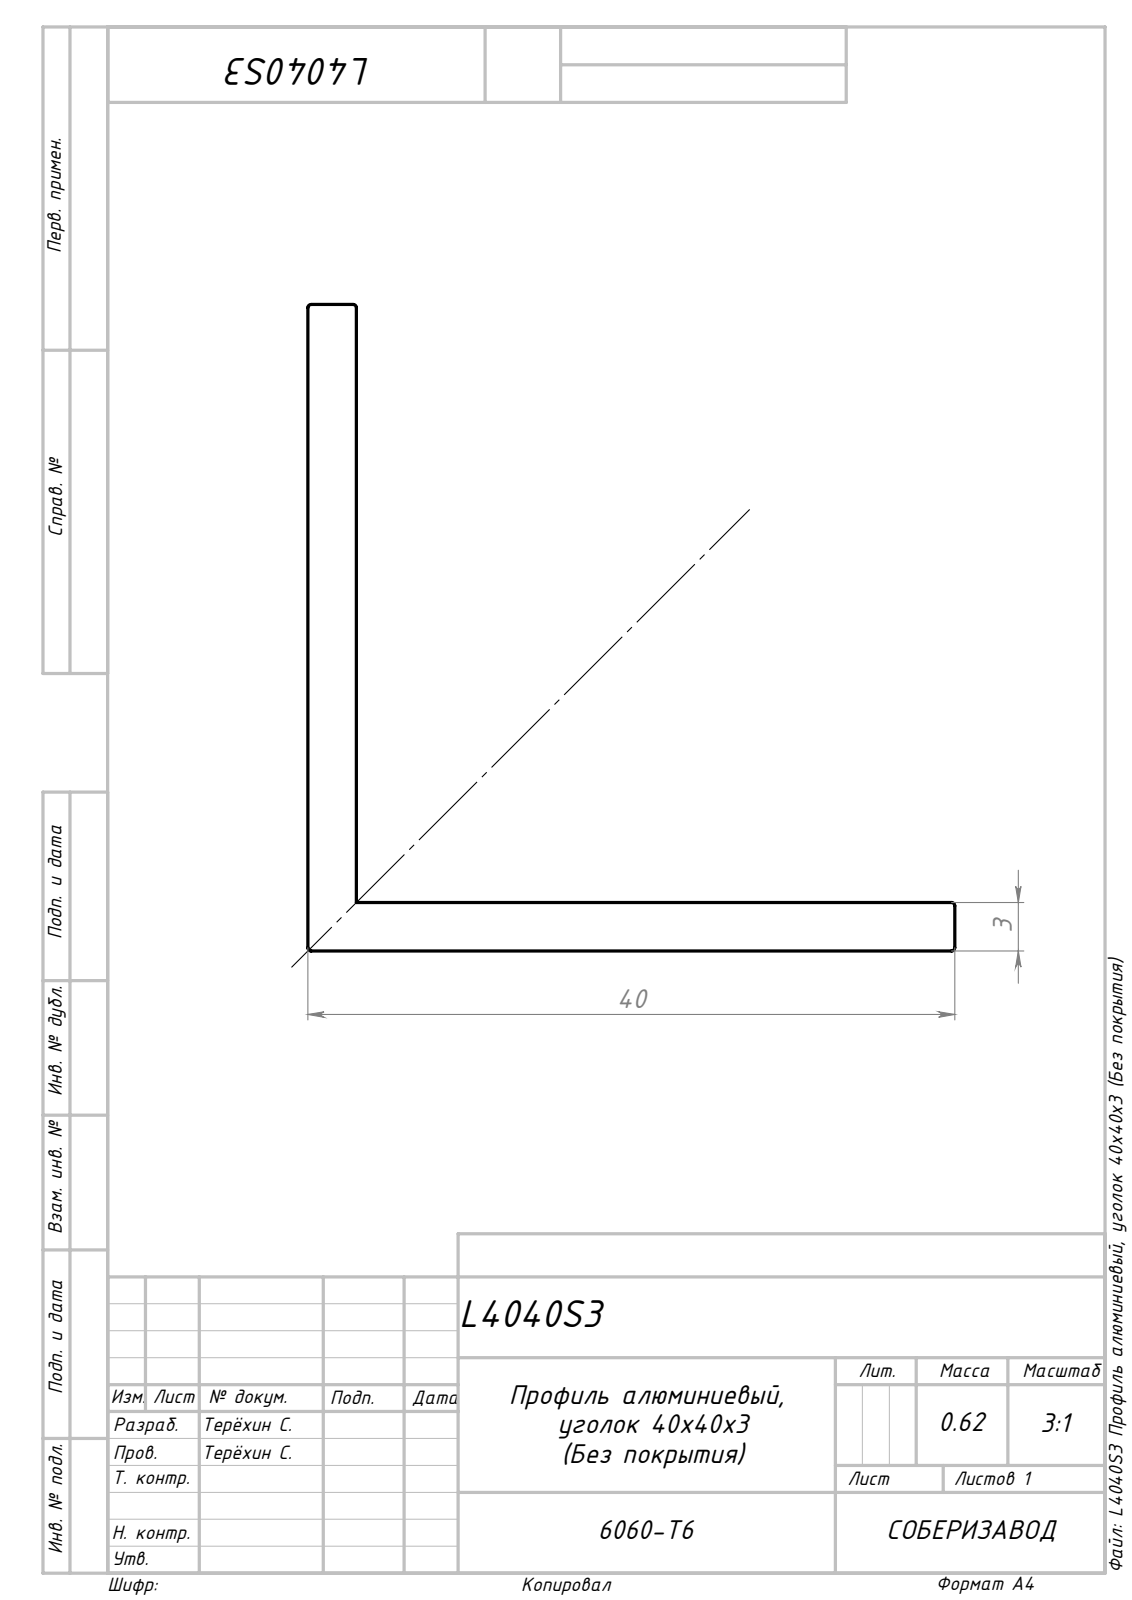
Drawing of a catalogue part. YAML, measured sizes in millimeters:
part_name: "L4040S3 Профиль алюминиевый, уголок 40x40x3 (Без покрытия)_00; Сборка7"
step_written_by: "SolidWorks 2024 (AUTOMOTIVE_DESIGN)"
units: millimeters
bodies: {solids: 1, faces: 13, planar: 8, cylindrical: 5, other: 0}
overall_size: [1000, 40, 40]
volume: 230957
surface_area: 160033
partial_cylinders:
  - {radius: 0.2, count: 5}
face_to_face_distances: [3, 40, 37, 1000]
